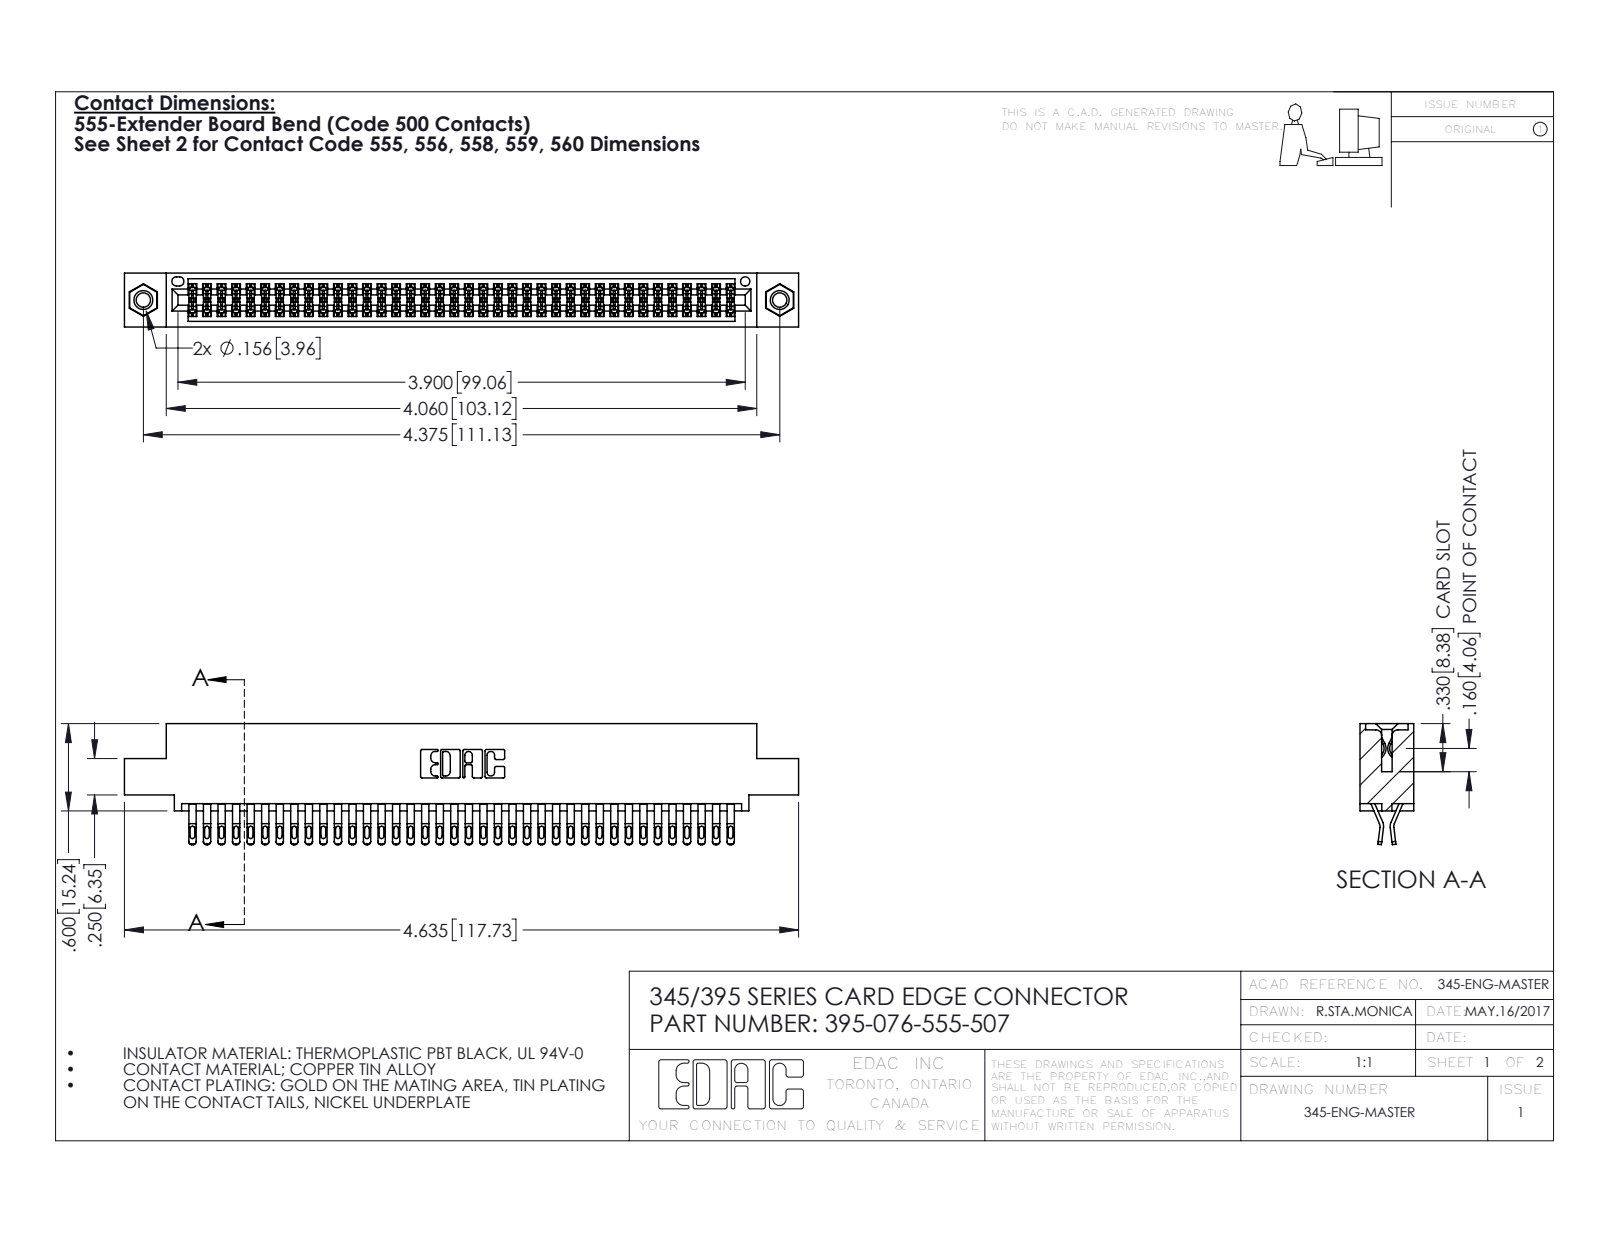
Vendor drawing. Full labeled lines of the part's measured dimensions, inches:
Part name (STEP PRODUCT): 345 Part_0.110 Offset - 0.156 Dia-TI; 395-076-555-507; 345-250-001_345-250-005-103; 345-292-001_555 Tail
STEP written by: SolidWorks 2016 (CONFIG_CONTROL_DESIGN)
Units: inches
Bodies: 79 solids, 4446 faces (2472 planar, 1958 cylindrical, 16 other)
Overall size (bounding box): 4.635 × 0.832 × 0.37
Volume: 0.704 in³ · Surface area: 27.68 in²
Round holes (diameter × count): ⌀0.098 ×2, ⌀0.125 ×2, ⌀0.156 ×2, ⌀0.064 ×1
Round bosses / shafts (diameter × count): ⌀0.155 ×2
Partial cylindrical surfaces — rounded edges, fillets, slot ends (radius × count): R0.016 ×190, R0.02 ×152, R0.006 ×114, R0.01 ×22, R0.007 ×6, R0.031 ×6, R0.026 ×3, R0.01 ×2
Main face-to-face distances: 0.072, 0.298, 0.025, 0.37, 0.2, 0.098, 0.272, 0.225, 0.175, 0.149
Hole centre spacings: 0.27, 4.139, 4.375
